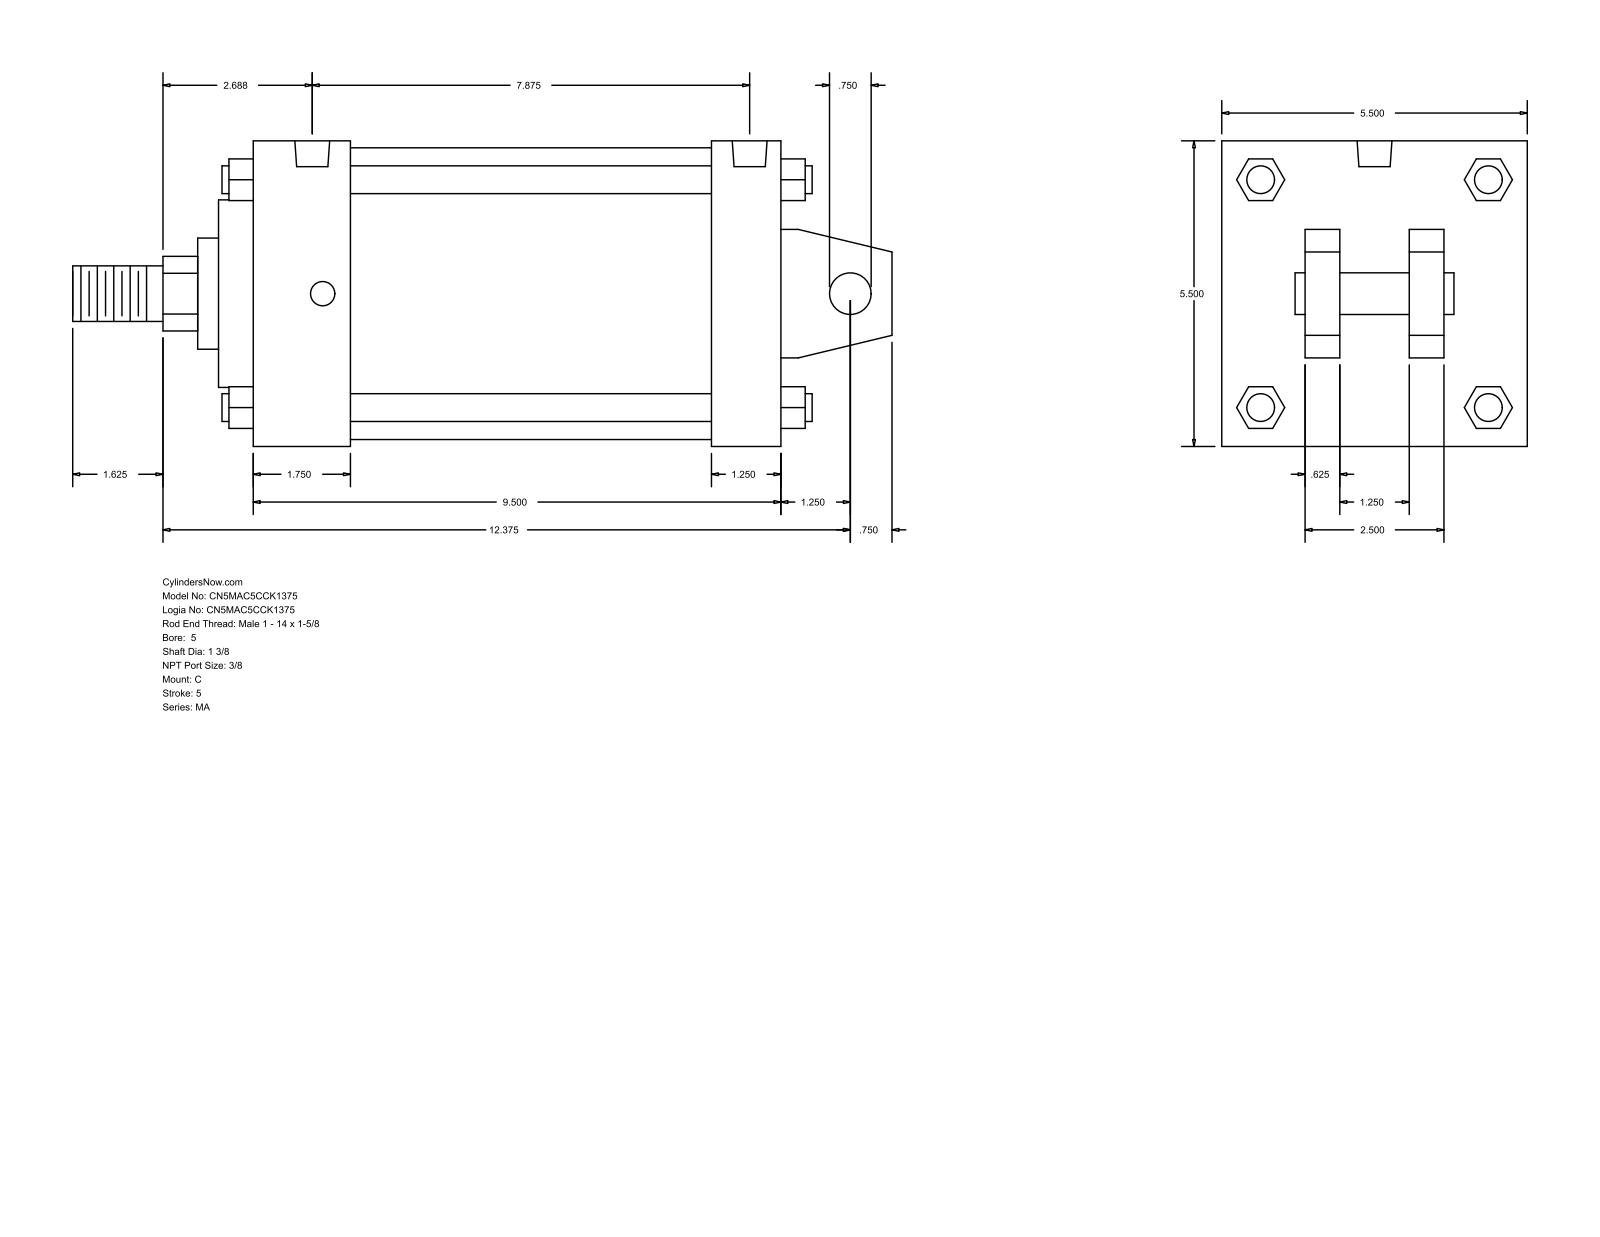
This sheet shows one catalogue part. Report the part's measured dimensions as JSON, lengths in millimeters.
{"part_name": "MA_C__0500_1.375", "step_written_by": "GSSL Pune (CONFIG_CONTROL_DESIGN)", "units": "millimeters", "bodies": {"solids": 0, "faces": 141, "planar": 109, "cylindrical": 32, "other": 0}, "overall_size": [374.65, 139.7, 139.7], "round_holes": [[11.11, 4], [15.93, 2]], "round_bosses_or_shafts": [[12.7, 4], [133.35, 1], [85.72, 1], [50.8, 1], [34.92, 1], [25.4, 1], [19.05, 1]], "partial_cylinders_radius": [[17.06, 1]], "face_to_face_distances": [139.7, 241.3, 15.87, 209.55, 31.75, 44.45, 165.1, 196.85, 53.97, 38.1], "hole_center_spacings": [4.77, 190.49, 195.26, 200.03]}
